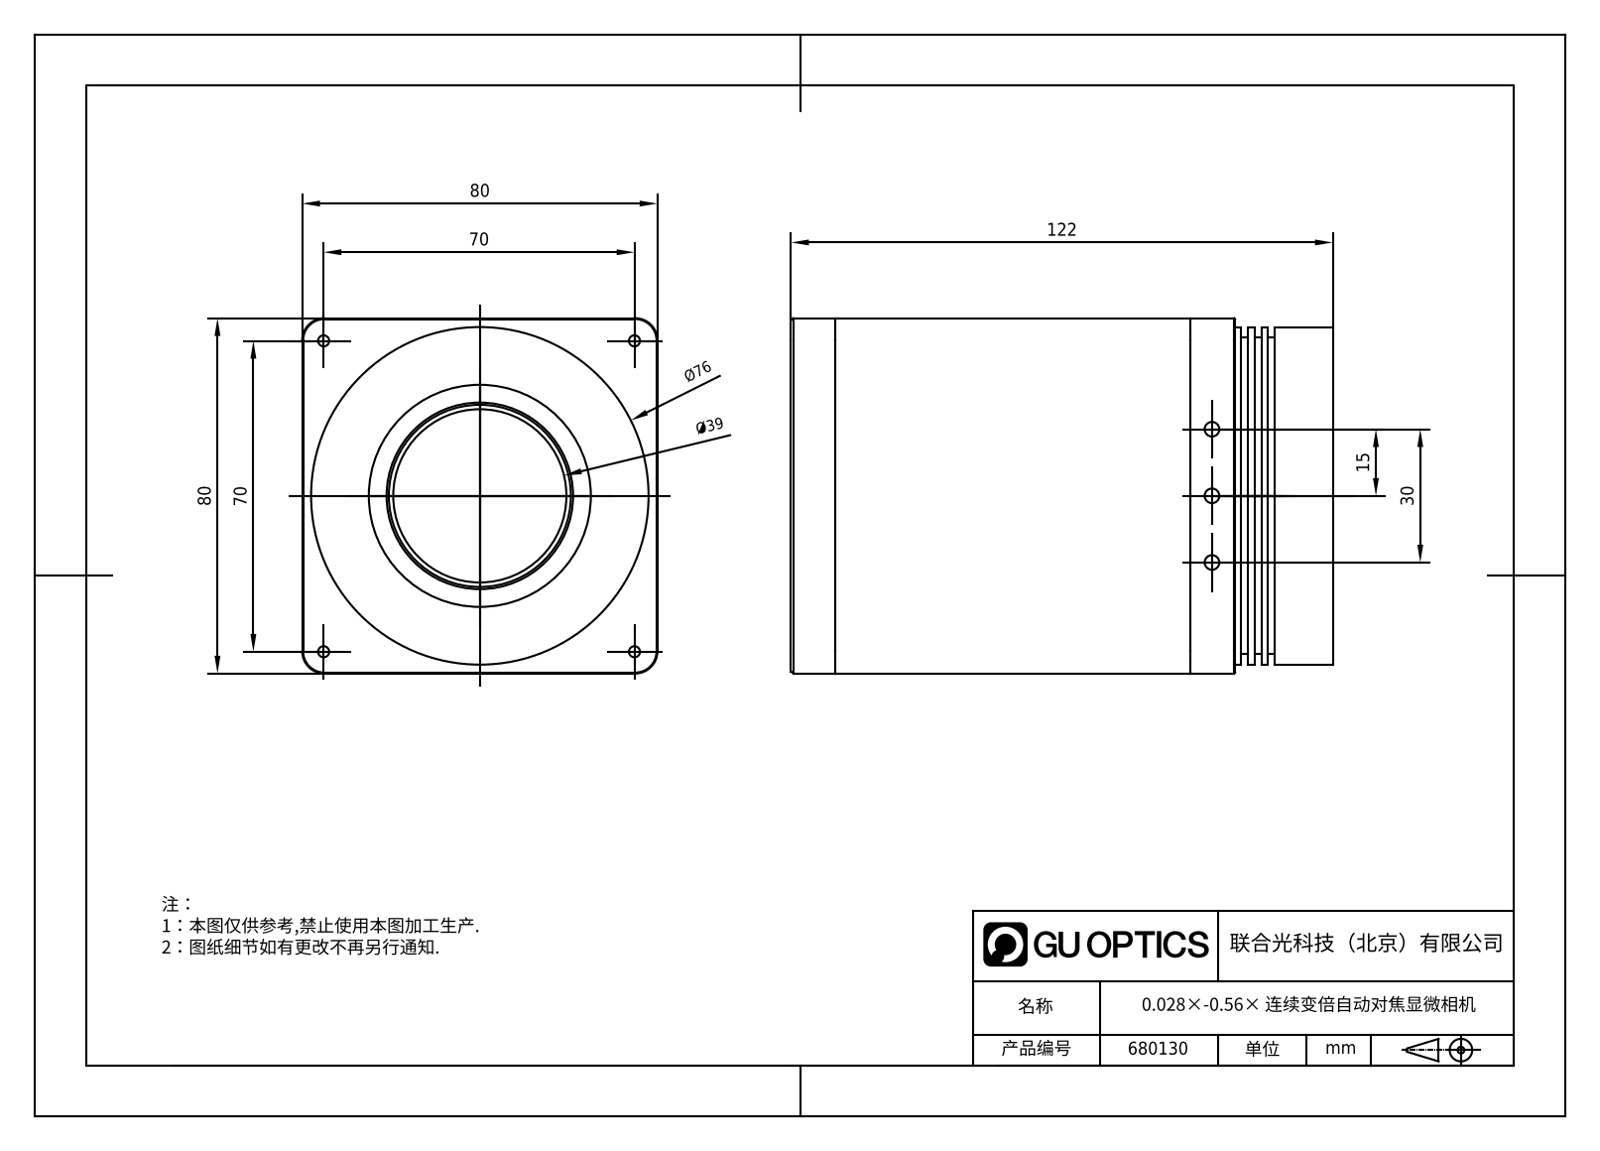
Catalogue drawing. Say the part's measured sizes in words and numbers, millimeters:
The part is named "680129". Its 3-D file was written by "SolidWorks 2020 (CONFIG_CONTROL_DESIGN)". It is 6 solids with 128 faces: 73 planar, 36 cylindrical and 19 other. Overall it measures 122 by 80 by 80 millimeters. Its volume is 710 475 cubic millimeters and its surface area 91 808 square millimeters. Round holes: 4 of diameter 2.5, 3 of diameter 3.3, 1 of diameter 8, 1 of diameter 39, 1 of diameter 50. Round bosses or shafts: 1 of diameter 76, 1 of diameter 71.23, 1 of diameter 64, 1 of diameter 42. Partial cylindrical surfaces (rounded edges, fillets, slot ends): 4 of radius 5, 2 of radius 1.83. The main face-to-face distances are 80, 10, 90, 100, 3, 1.5, 22, 32, 112, 122. The hole center spacings are 70, 15, 98.99, 15.36, 30, 34.19, 49.31, 49.45.
